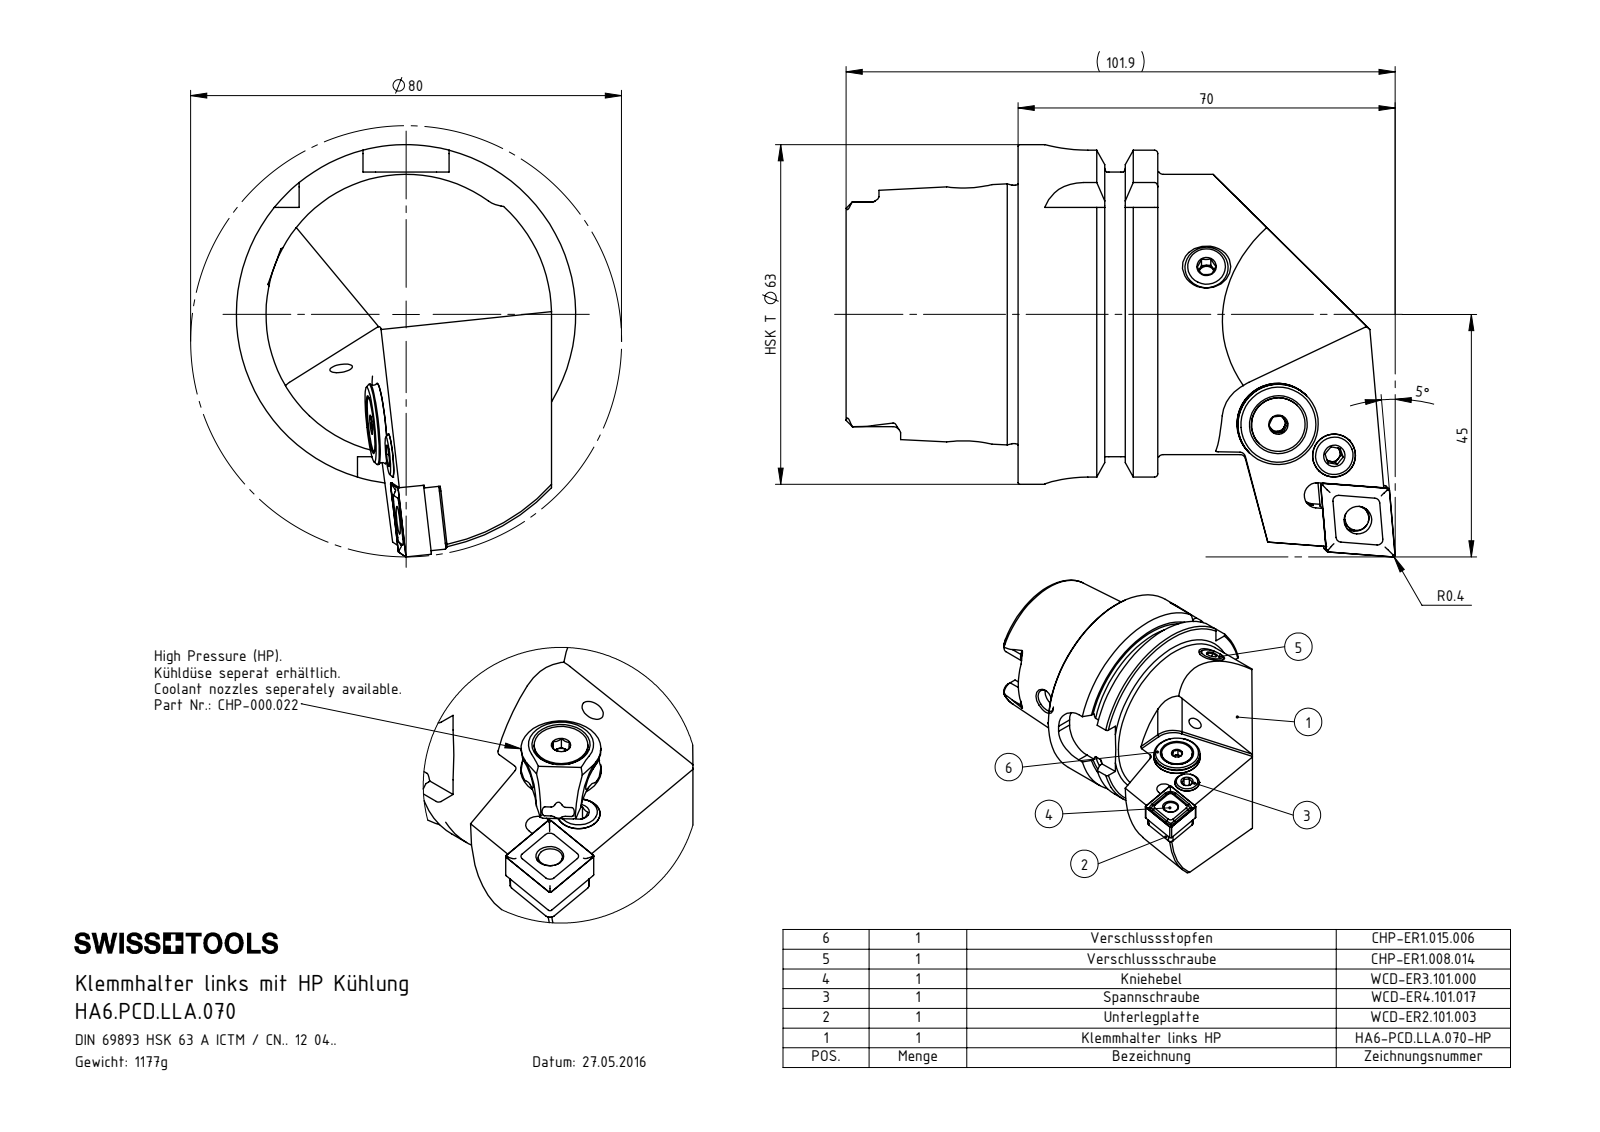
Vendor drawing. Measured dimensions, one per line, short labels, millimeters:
name: HA6-PCD.LLA.070; KVT_MB_600_060; WCD; WCD-ER3.101.000_A (+4 more)
written by: SolidWorks 2012 (CONFIG_CONTROL_DESIGN)
unit: mm
bodies: 7 solids, 371 faces (118 planar, 105 cylindrical, 148 other)
size: 101.9 × 76.5 × 63
volume: 144 823 mm³; area: 32 888 mm²
holes: 3× ⌀5, 2× ⌀8.4, 1× ⌀5.16, 1× ⌀6, 1× ⌀6.4, 1× ⌀7, 1× ⌀7.5, 1× ⌀10, 1× ⌀17, 1× ⌀19, 1× ⌀34, 1× ⌀40
bosses: 1× ⌀63, 1× ⌀54.95, 1× ⌀52, 1× ⌀47.94, 1× ⌀8, 1× ⌀7.9, 1× ⌀6.4, 1× ⌀6
rounds: 6× R1.4, 4× R0.4, 4× R1, 4× R8, 2× R2.5, 2× R2.82, 2× R2.88, 1× R2.1
face distances: 25.95, 16, 9.95, 31.9, 41.85, 57.85, 52.8, 21.8, 11.85, 4.15
hole spacings: 12.8, 12.85
